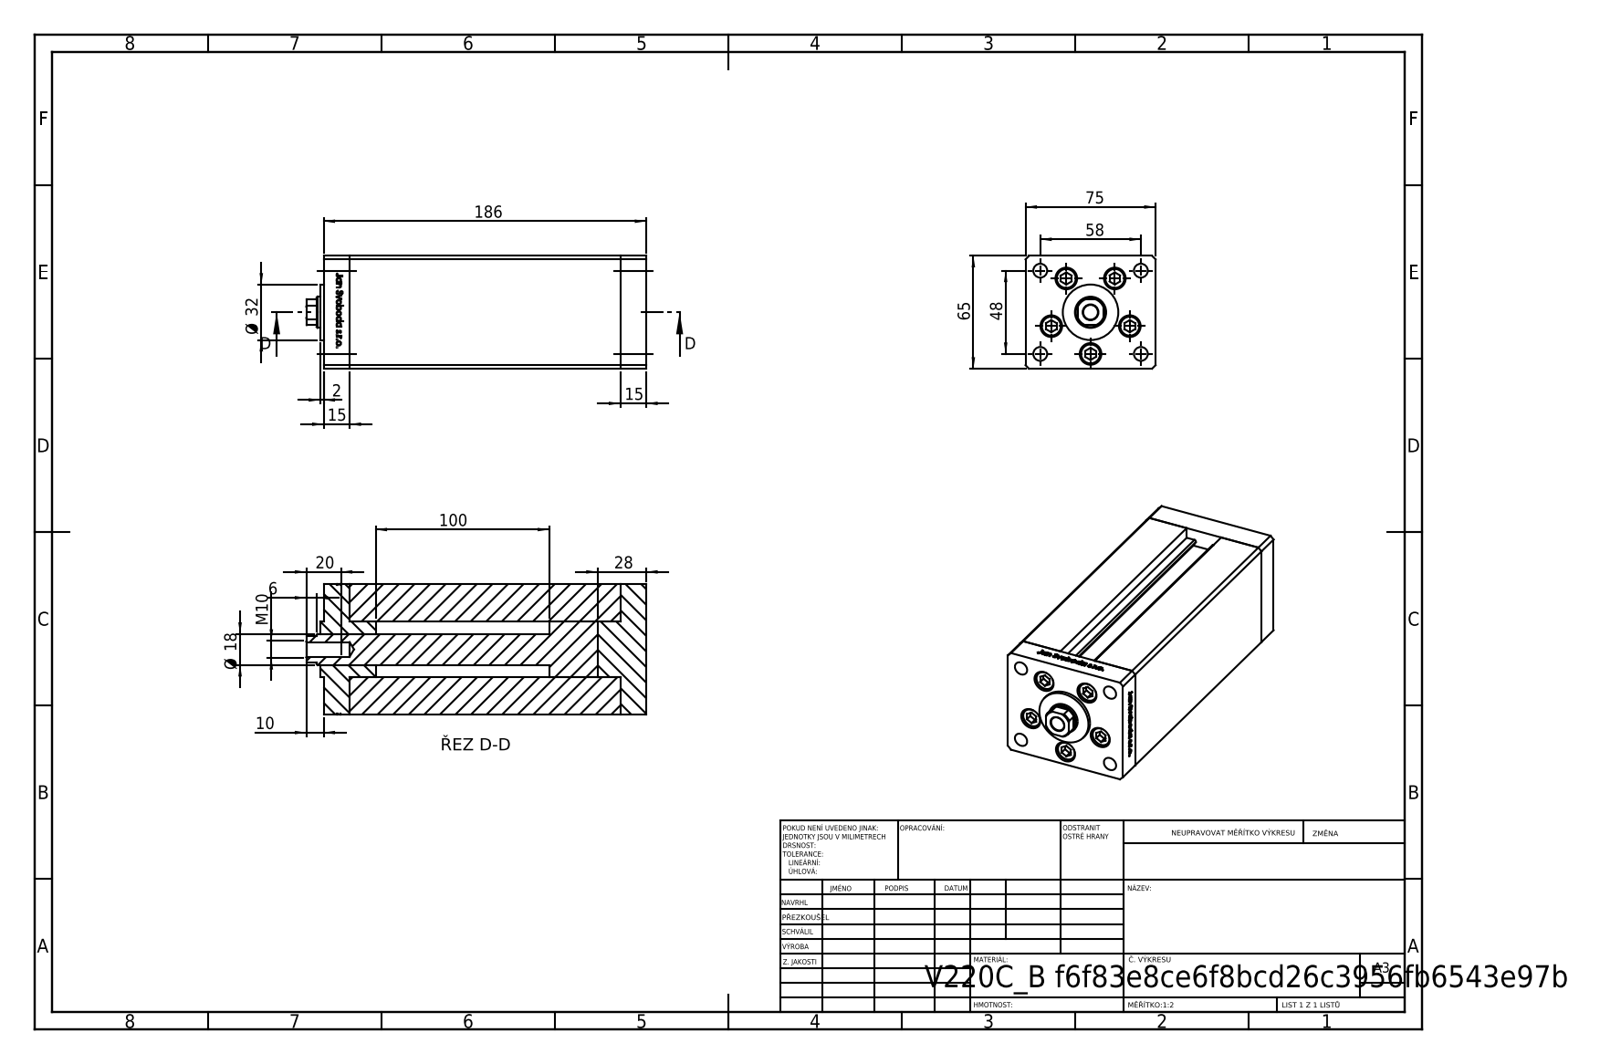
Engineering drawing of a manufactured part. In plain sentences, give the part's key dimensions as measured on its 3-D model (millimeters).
The part is named "V220C_VC_B; V220C_B MIDDLE; V220C BACK_B; ALLEN BOLT (+1 more)". Its 3-D file was written by "SolidWorks 2019 (CONFIG_CONTROL_DESIGN)". It is 14 solids with 1183 faces: 462 planar, 147 cylindrical and 574 other. Overall it measures 196 by 75 by 65 millimeters. Its volume is 804 978 cubic millimeters and its surface area 136 497 square millimeters. Round holes: 5 of diameter 9, 5 of diameter 12.5, 4 of diameter 8, 2 of diameter 2, 2 of diameter 13.16, 1 of diameter 8.5, 1 of diameter 18. Round bosses or shafts: 5 of diameter 8, 1 of diameter 32. Partial cylindrical surfaces (rounded edges, fillets, slot ends): 2 of radius 0.93, 1 of radius 8.5. The main face-to-face distances are 75, 65, 15, 156, 171, 186, 28, 54.5, 10.5, 26.25. The hole center spacings are 24, 37.64, 15.67, 17.22, 27.71, 28.83, 29, 32.63.
